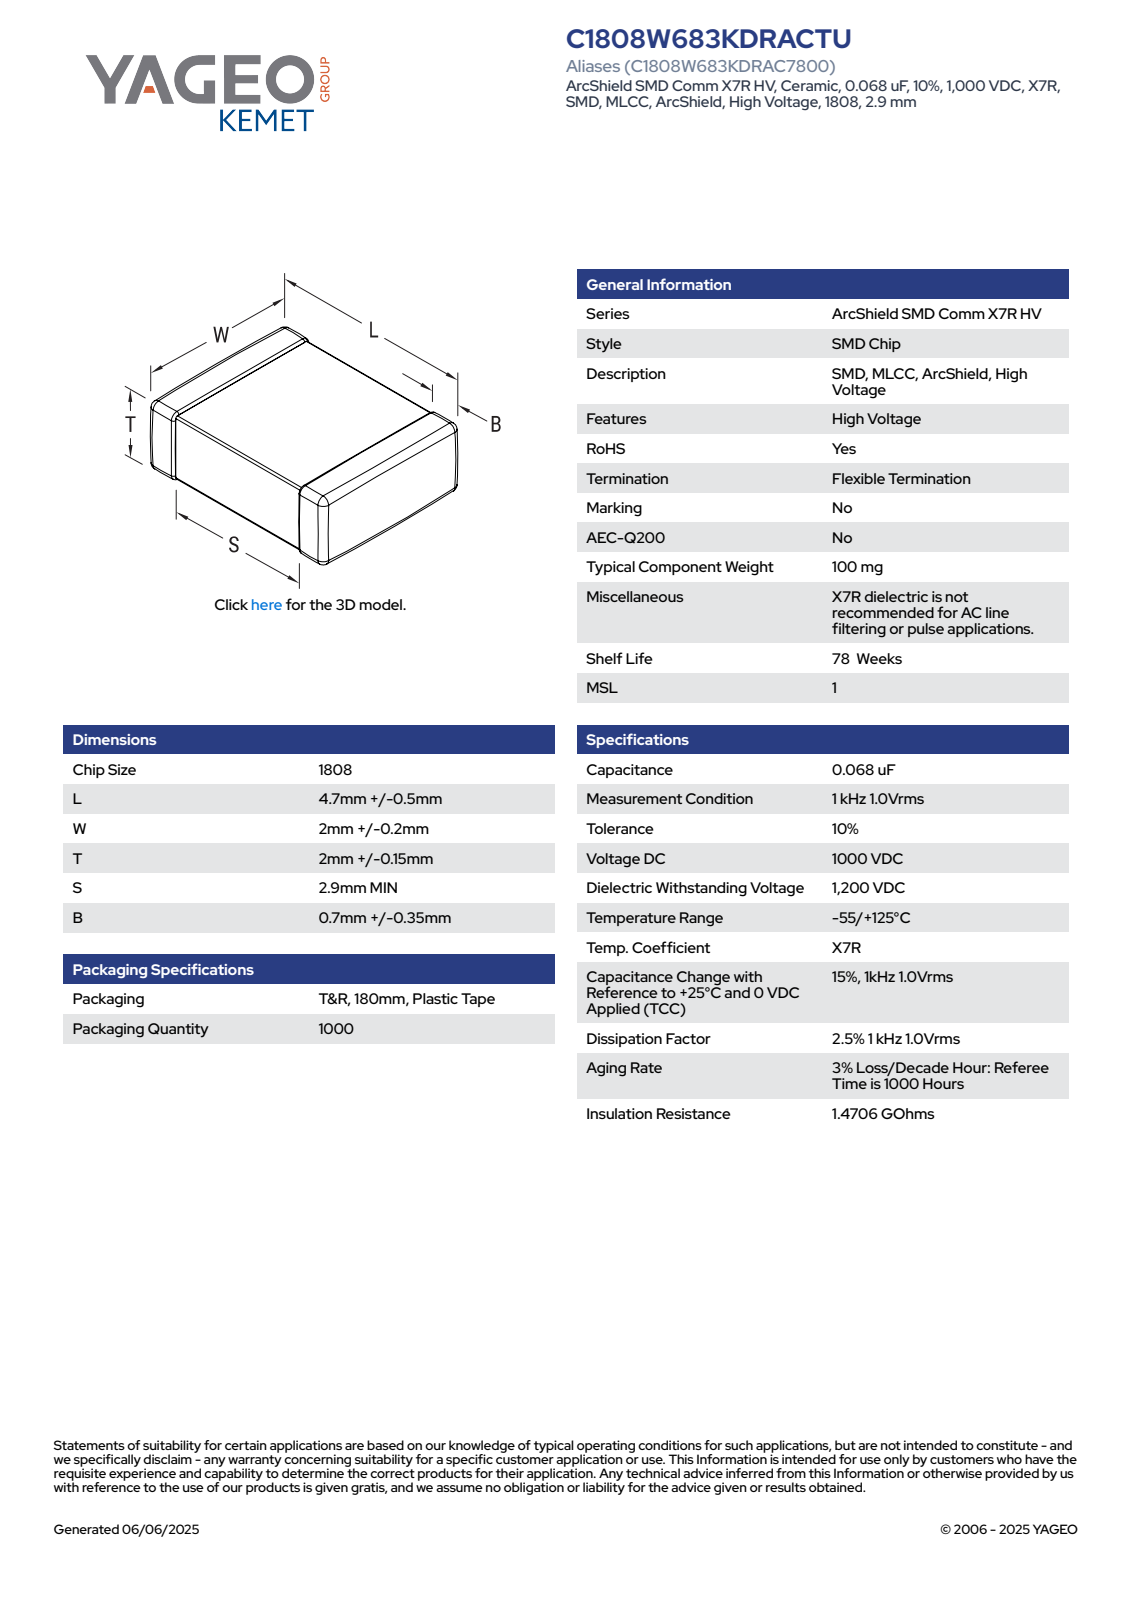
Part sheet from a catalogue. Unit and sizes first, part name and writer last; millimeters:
Units: millimetres
Overall size (bounding box): 5.2 × 2.2 × 2.15
Main face-to-face distances: 2.1, 2.15, 2.05, 5.2, 2.2, 2.11, 2.06, 0.89, 1.26, 0.37
Volume: 23 mm³ · Surface area: 54 mm²
Bodies: 4 solids, 125 faces (71 planar, 38 cylindrical, 16 other)
Part name (STEP PRODUCT): CCS_CCSTDNOS_1808_L5.2W2.2T2.15B1.05
STEP written by: SolidWorks 2014 (AUTOMOTIVE_DESIGN)
